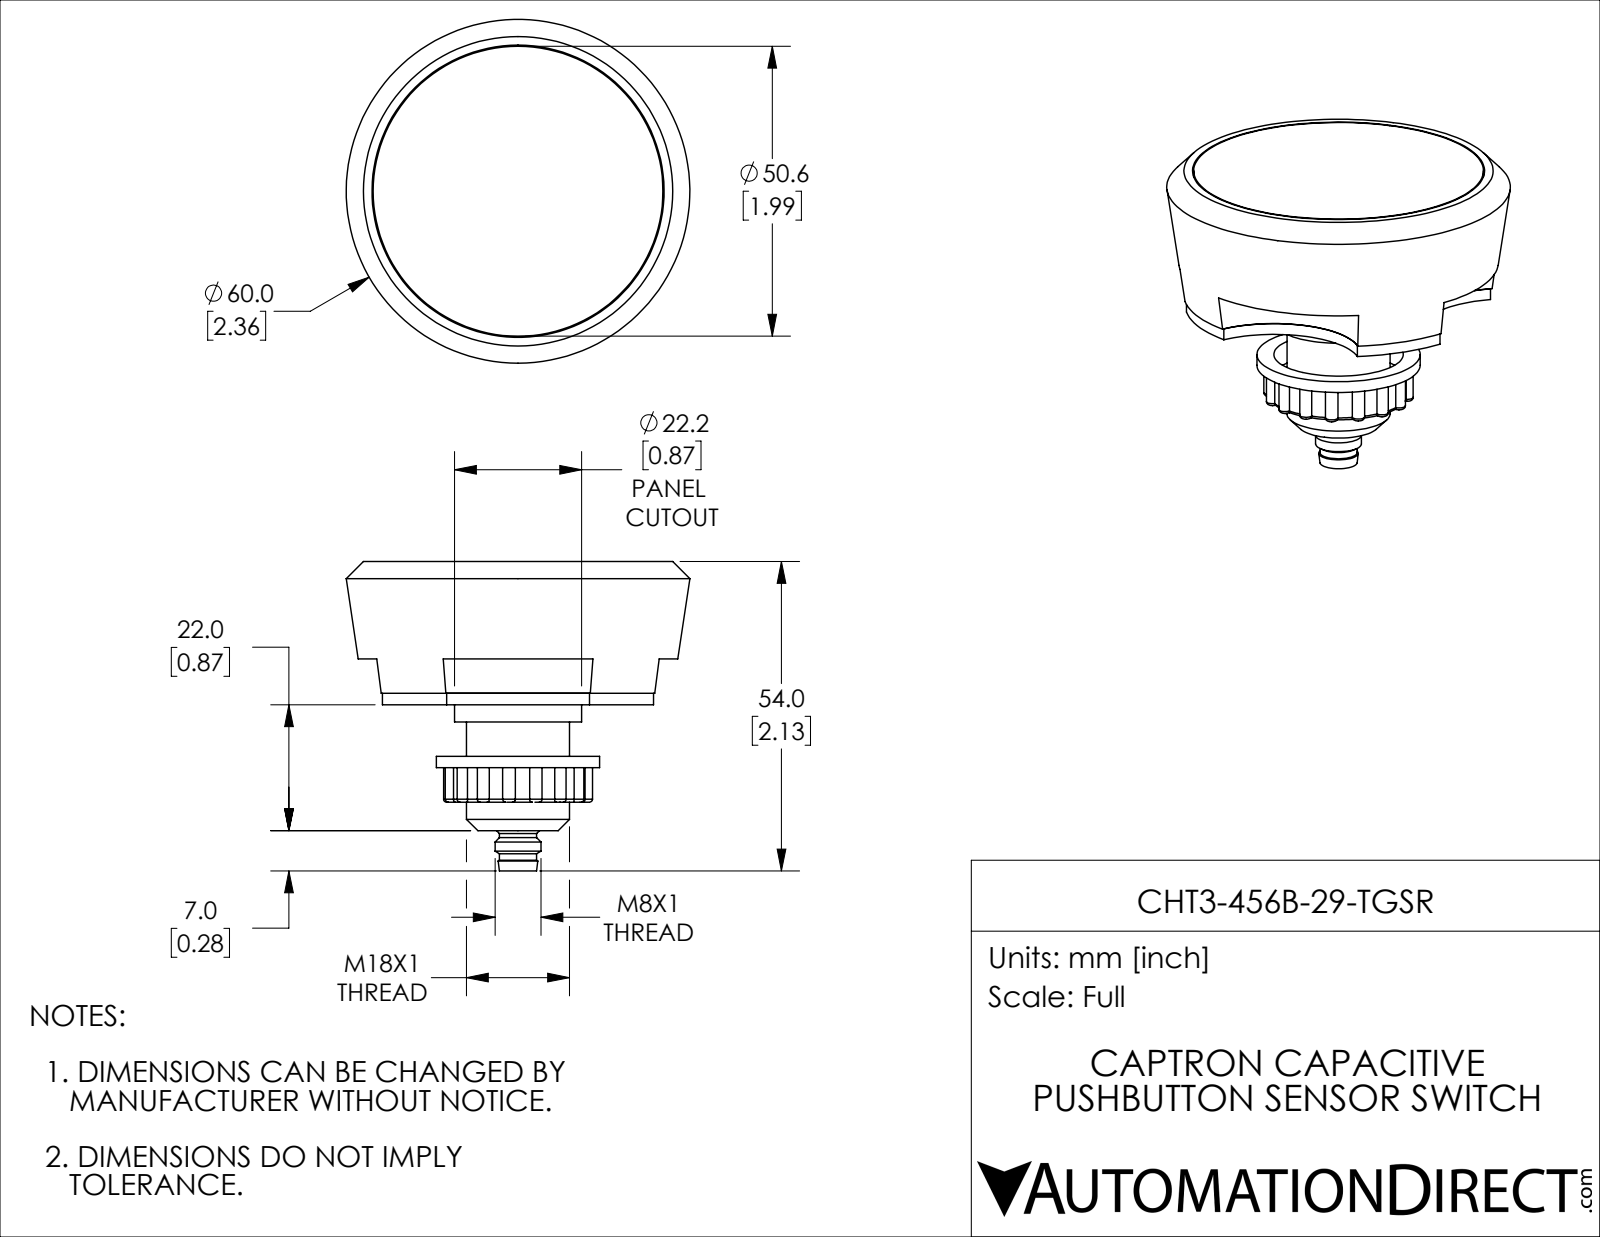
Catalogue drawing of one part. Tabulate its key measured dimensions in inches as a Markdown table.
| quantity | value |
| --- | --- |
| part name | CHT3-456B-29-TGSR |
| STEP written by | SolidWorks 2019 (CONFIG_CONTROL_DESIGN) |
| units | inches |
| bodies | 10 solids, 200 faces (28 planar, 94 cylindrical, 78 other) |
| overall size | 2.362 × 2.362 × 2.126 |
| volume | 3.853 in³ |
| surface area | 32.45 in² |
| round holes (diameter × count) | 0.669 × 1, 0.89 × 1, 2.008 × 1 |
| round bosses / shafts (diameter × count) | 0.039 × 5, 1.992 × 1, 1.122 × 1, 0.874 × 1, 0.709 × 1, 0.315 × 1, 0.256 × 1 |
| partial cylindrical surfaces (radius × count) | 0.043 × 16, 0.591 × 4, 0.02 × 2, 0.039 × 1, 0.114 × 1, 0.472 × 1, 1.053 × 1 |
| main face-to-face distances | 0.906, 0.091, 0.815, 0.134, 0.772, 0.043, 0.079, 0.984, 0.669, 0.85 |
